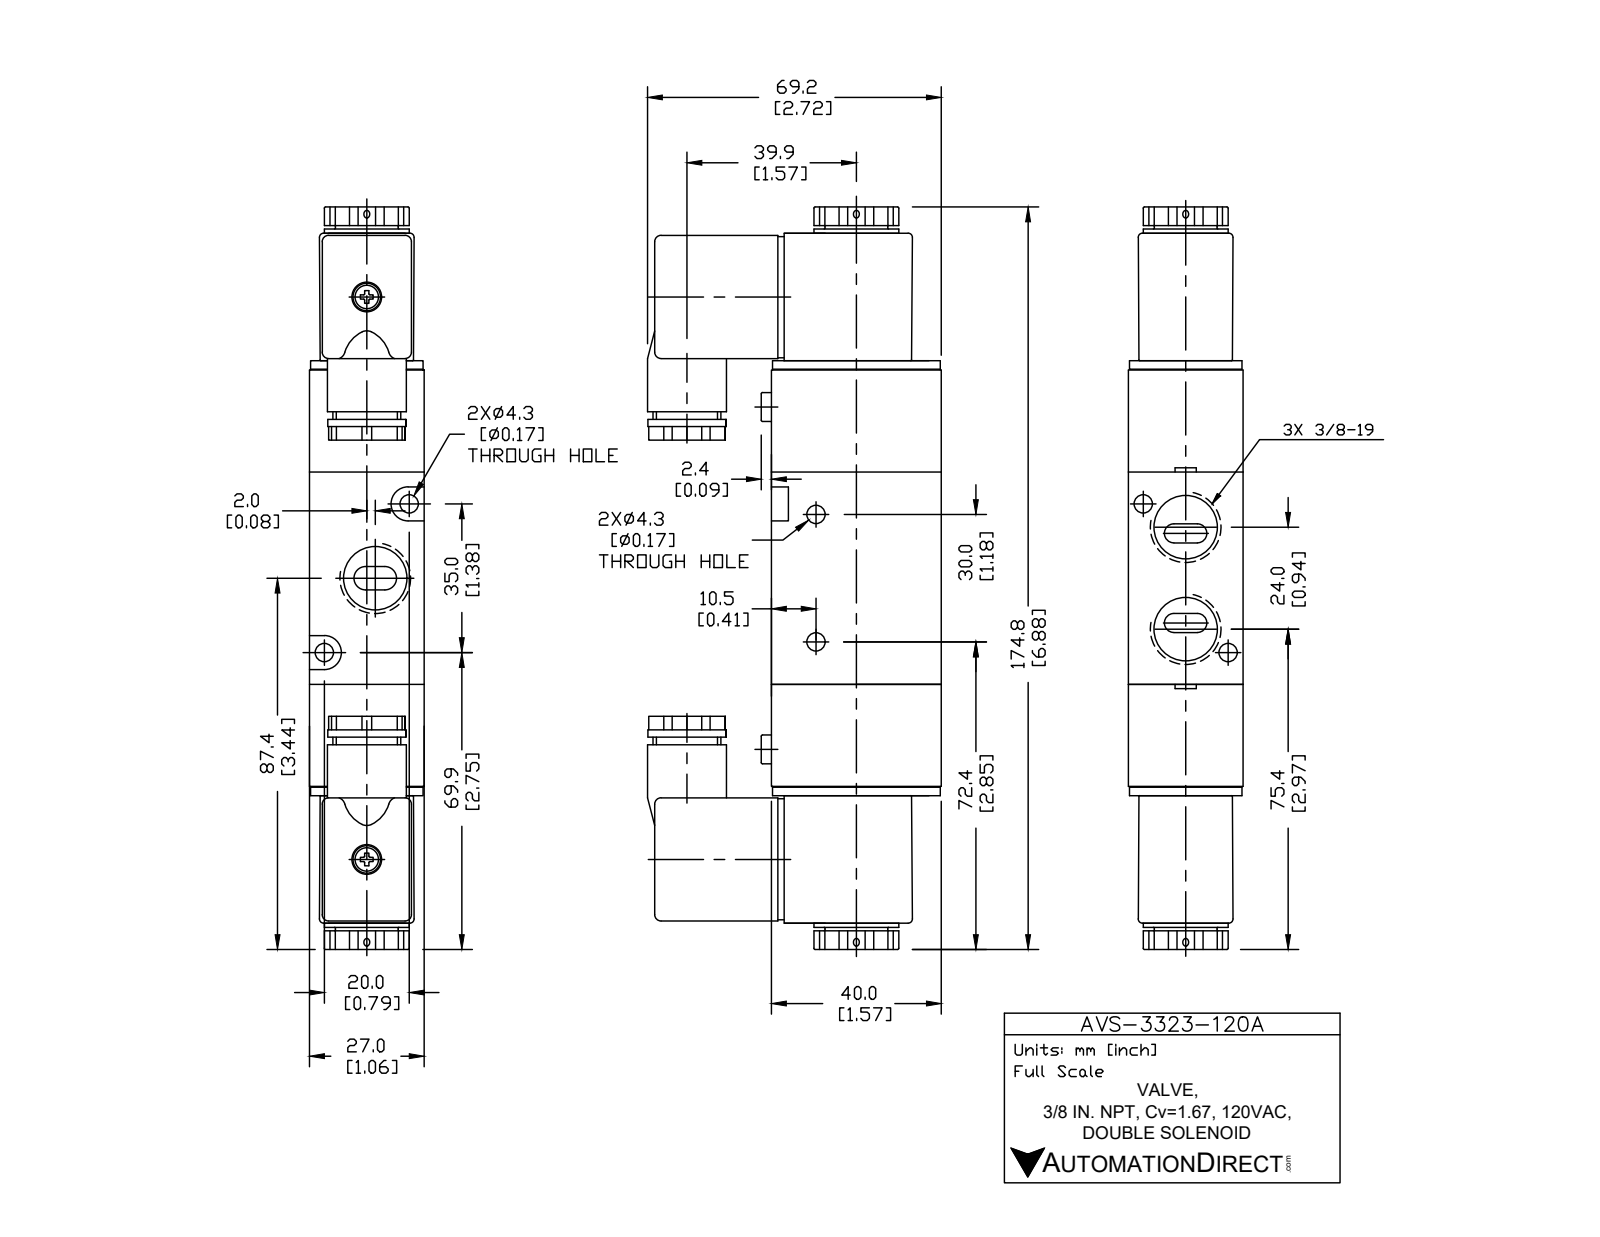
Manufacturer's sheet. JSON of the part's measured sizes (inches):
{"part_name": "AVS-3323-120A", "step_written_by": "SolidWorks 2015 (CONFIG_CONTROL_DESIGN)", "units": "inches", "bodies": {"solids": 5, "faces": 246, "planar": 132, "cylindrical": 82, "other": 32}, "overall_size": [6.882, 2.72, 1.063], "volume_in3": 11.48, "surface_area_in2": 62.73, "round_holes": [[0.169, 4], [0.562, 3], [0.366, 1]], "round_bosses_or_shafts": [[0.268, 2], [0.787, 1], [0.732, 1], [0.724, 1], [0.63, 1], [0.583, 1]], "partial_cylinders_radius": [[0.039, 20], [0.02, 12], [0.157, 2]], "face_to_face_distances": [0.118, 0.945, 1.969, 1.081, 1.063, 0.827, 0.992, 0.089, 0.089, 0.902], "hole_center_spacings": [0.449, 0.479, 1.226, 0.757, 0.835, 0.945, 1.181, 1.587]}
